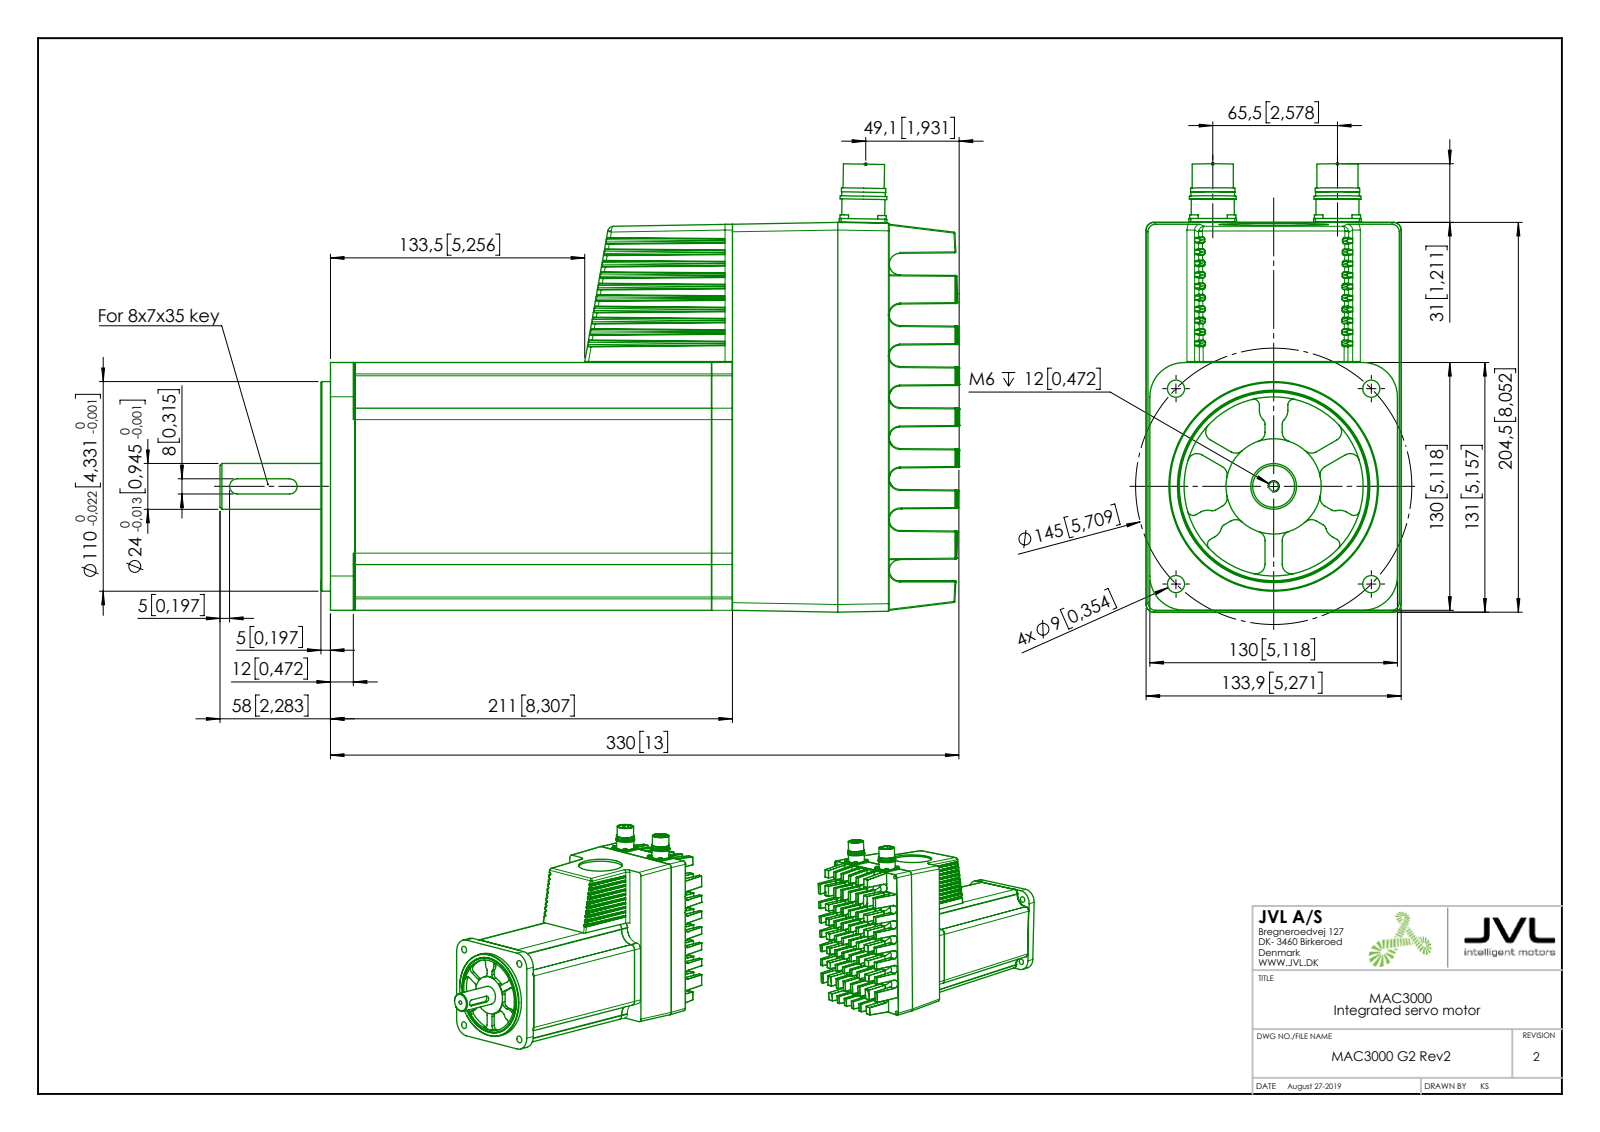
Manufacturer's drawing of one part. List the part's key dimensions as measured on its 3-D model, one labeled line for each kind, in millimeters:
Part name (STEP PRODUCT): MAC3000 G2 Rev2; Rear flange S; Center part S_MAC3000; Housing S (+6 more)
STEP written by: SolidWorks 2018 (AUTOMOTIVE_DESIGN)
Units: millimetres
Bodies: 9 solids, 2395 faces (733 planar, 981 cylindrical, 681 other)
Overall size (bounding box): 388.28 × 235.27 × 133.88
Volume: 6 022 000 mm³ · Surface area: 511 325 mm²
Round holes (diameter × count): ⌀2.5 ×8, ⌀2 ×5, ⌀4.3 ×4, ⌀9 ×4, ⌀20 ×2, ⌀20.2 ×2, ⌀4.6 ×1, ⌀5 ×1, ⌀57.62 ×1, ⌀94 ×1, ⌀100 ×1, ⌀117 ×1
Round bosses / shafts (diameter × count): ⌀4.5 ×8, ⌀2 ×4, ⌀24.5 ×2, ⌀23.3 ×2, ⌀22.9 ×2, ⌀22.6 ×2, ⌀21.6 ×2, ⌀112 ×1
Partial cylindrical surfaces — rounded edges, fillets, slot ends (radius × count): R0.5 ×297, R0.3 ×90, R0.8 ×40, R5 ×18, R3 ×15, R4 ×12, R0.6 ×10, R6 ×8
Main face-to-face distances: 55.3, 130, 198, 253.3, 187, 11, 66.3, 21.5, 48.02, 200
Hole centre spacings: 14.14, 20, 65.48, 6, 7.05, 28.28, 56.37, 68.47
